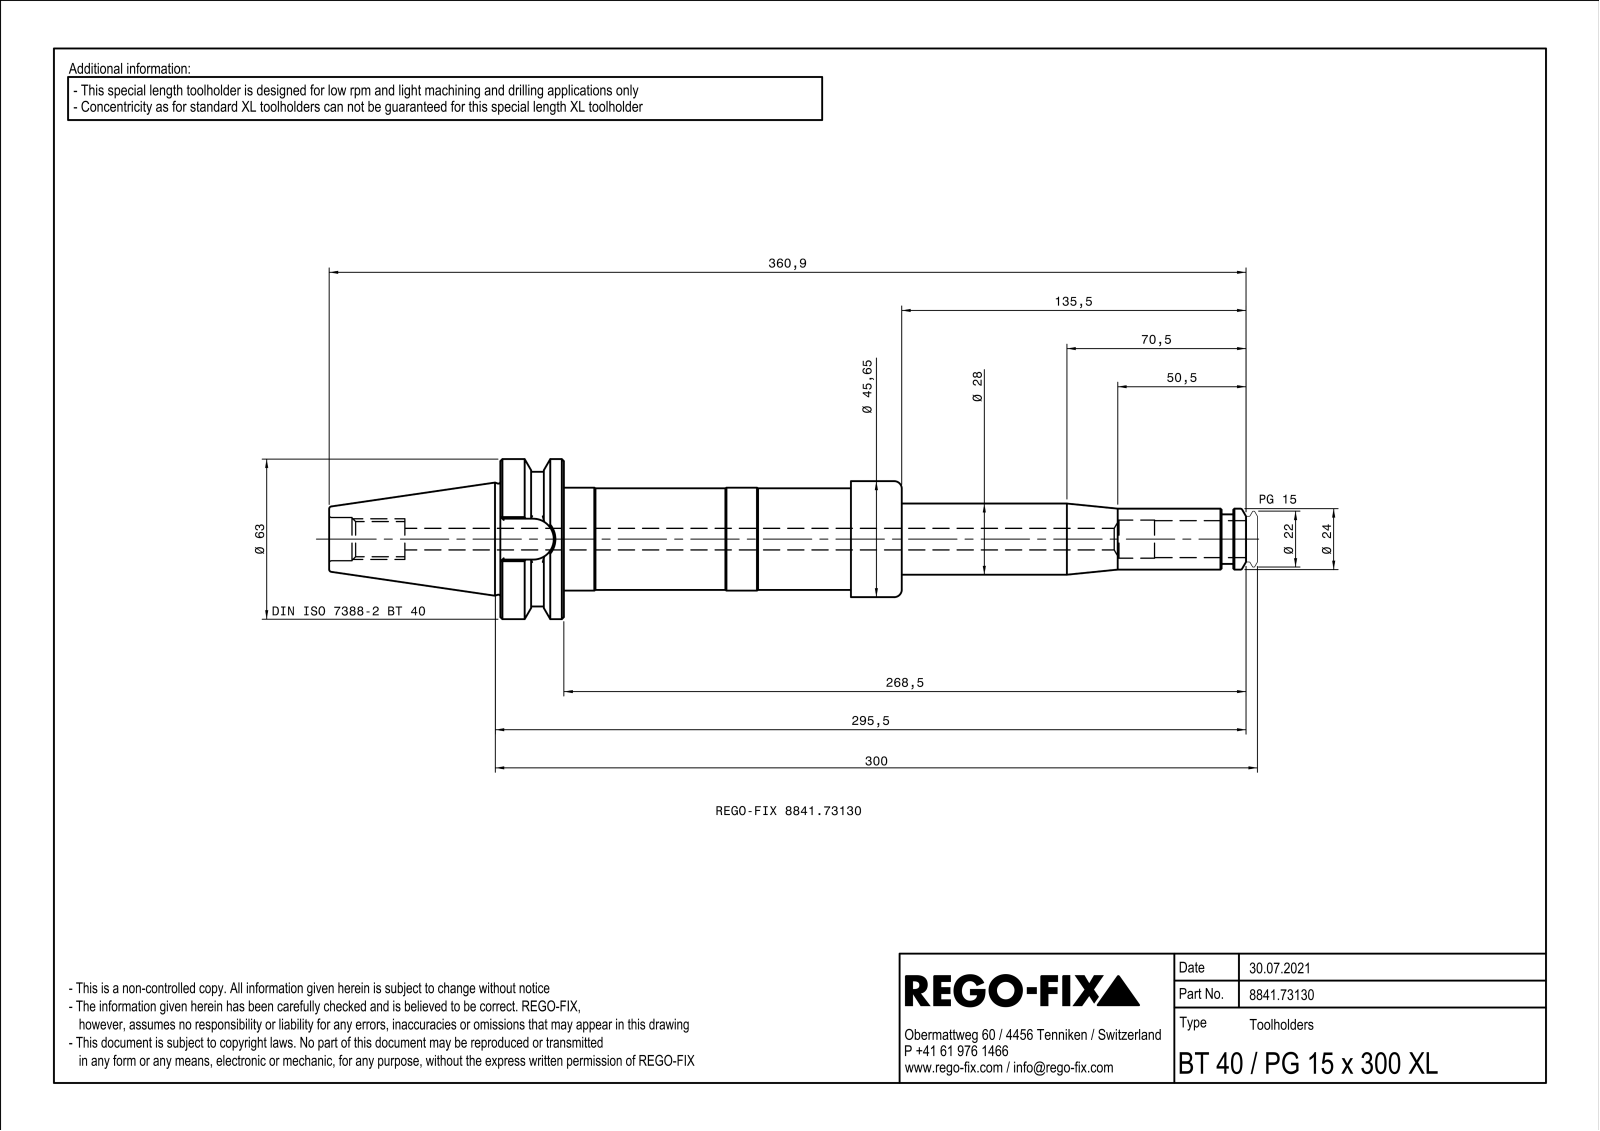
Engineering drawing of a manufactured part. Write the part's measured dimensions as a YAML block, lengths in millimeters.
part_name: "NOCUT"
step_written_by: "SIEMENS PLM Software Solid Edge ST10 (AUTOMOTIVE_DESIGN)"
units: millimeters
bodies: {solids: 1, faces: 155, planar: 52, cylindrical: 37, other: 66}
overall_size: [360.9, 63, 63]
volume: 326135
surface_area: 68903
round_holes:
  - {diameter: 9, count: 1}
  - {diameter: 10, count: 1}
  - {diameter: 13, count: 1}
  - {diameter: 13.84, count: 1}
  - {diameter: 15, count: 1}
  - {diameter: 17, count: 1}
  - {diameter: 25, count: 1}
  - {diameter: 29, count: 1}
  - {diameter: 38.38, count: 1}
  - {diameter: 40.05, count: 1}
  - {diameter: 43.3, count: 1}
round_bosses_or_shafts:
  - {diameter: 63, count: 1}
  - {diameter: 53, count: 1}
  - {diameter: 45.65, count: 1}
  - {diameter: 40.5, count: 1}
  - {diameter: 40, count: 1}
  - {diameter: 34, count: 1}
  - {diameter: 33, count: 1}
  - {diameter: 28, count: 1}
partial_cylinders:
  - {radius: 0.5, count: 4}
  - {radius: 8.05, count: 1}
  - {radius: 22.77, count: 1}
face_to_face_distances: [25, 158, 133, 6, 14, 1.5, 131.5, 156.5, 20, 18.5]
